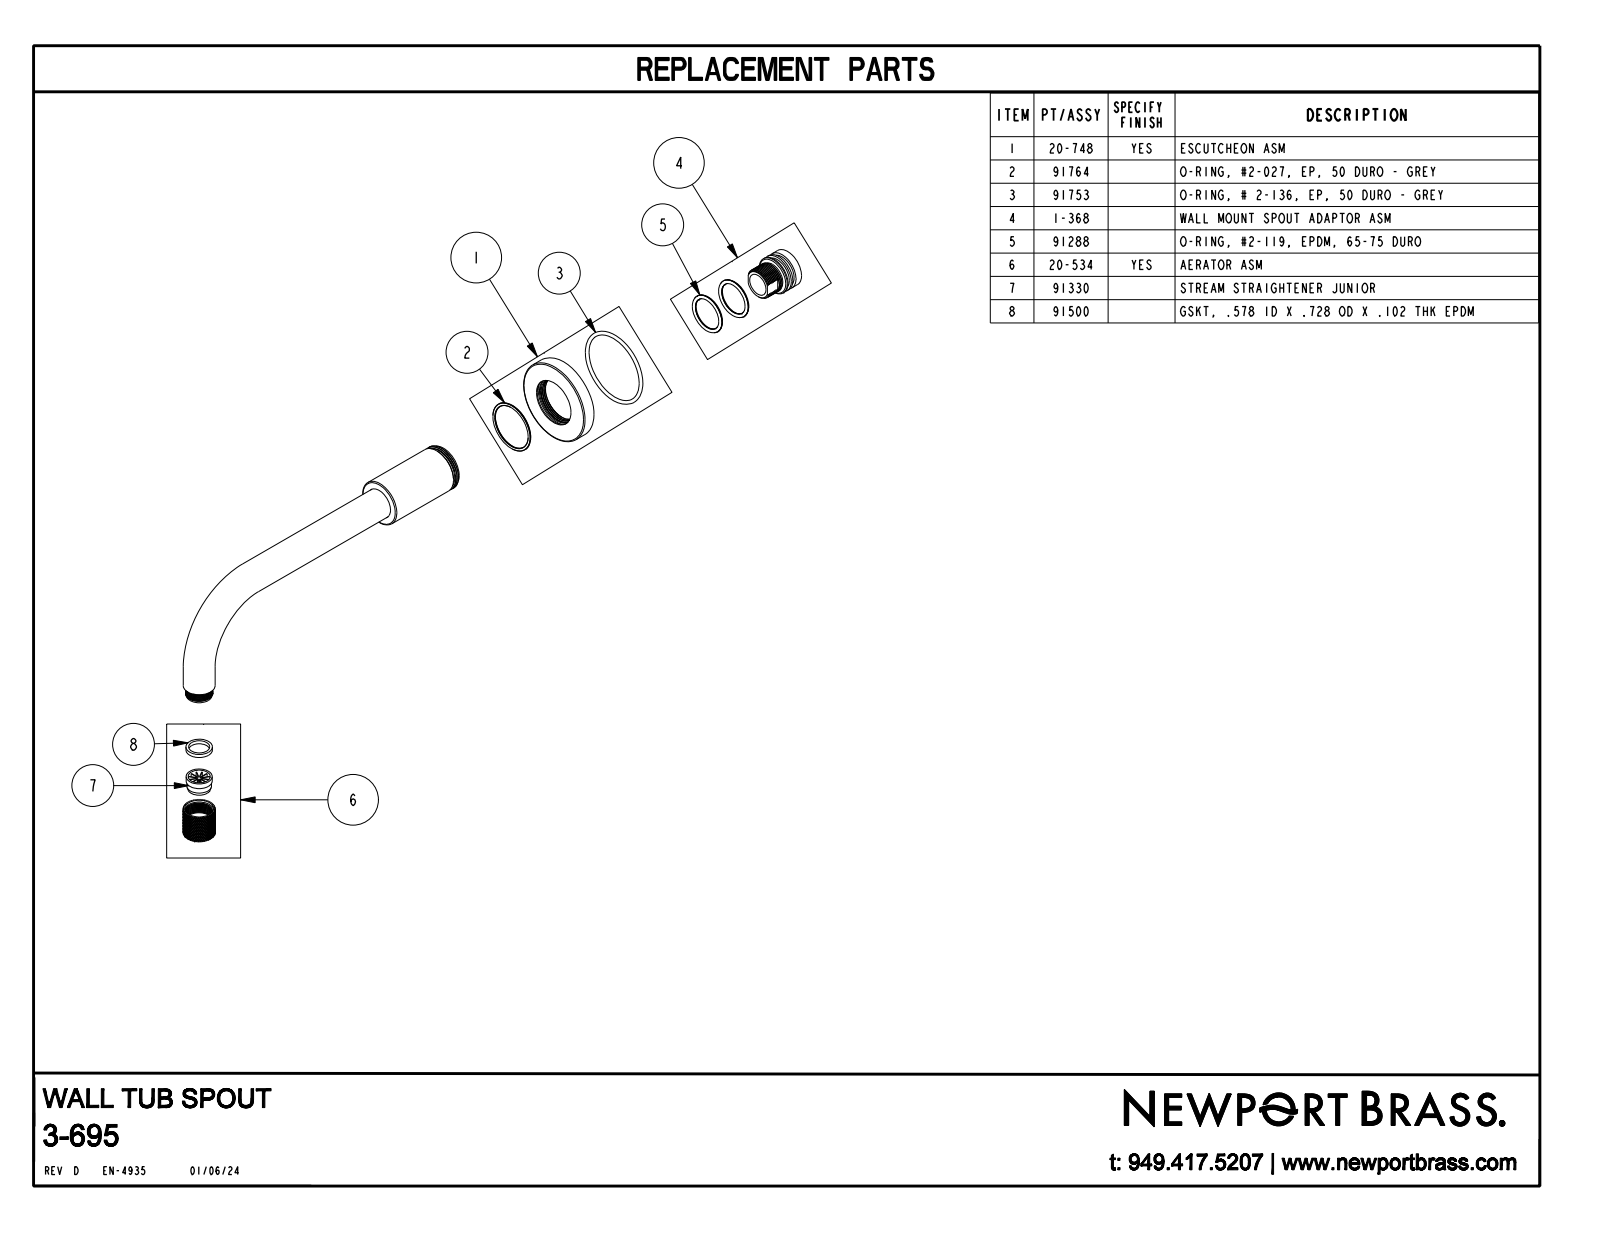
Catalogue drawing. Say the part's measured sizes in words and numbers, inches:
The part is named "3-695". Its 3-D file was written by "CREO PARAMETRIC BY PTC INC, 2019352 (CONFIG_CONTROL_DESIGN)". It is 1 solid with 4561 faces: 154 planar, 871 cylindrical and 3536 other. Overall it measures 9.938 by 4.628 by 2.375 inches. Its volume is 10.27 cubic inches and its surface area 47.79 square inches. Round holes: 1 of diameter 0.118, 1 of diameter 0.606, 1 of diameter 0.691. Round bosses or shafts: 2 of diameter 0.875, 1 of diameter 2.375, 1 of diameter 1.312, 1 of diameter 0.16. Partial cylindrical surfaces (rounded edges, fillets, slot ends): 1 of radius 0.3. The main face-to-face distances are 0.375, 2.5, 2.125, 0.06, 0.04, 0.02, 0.017, 0.033, 0.053, 0.017.
